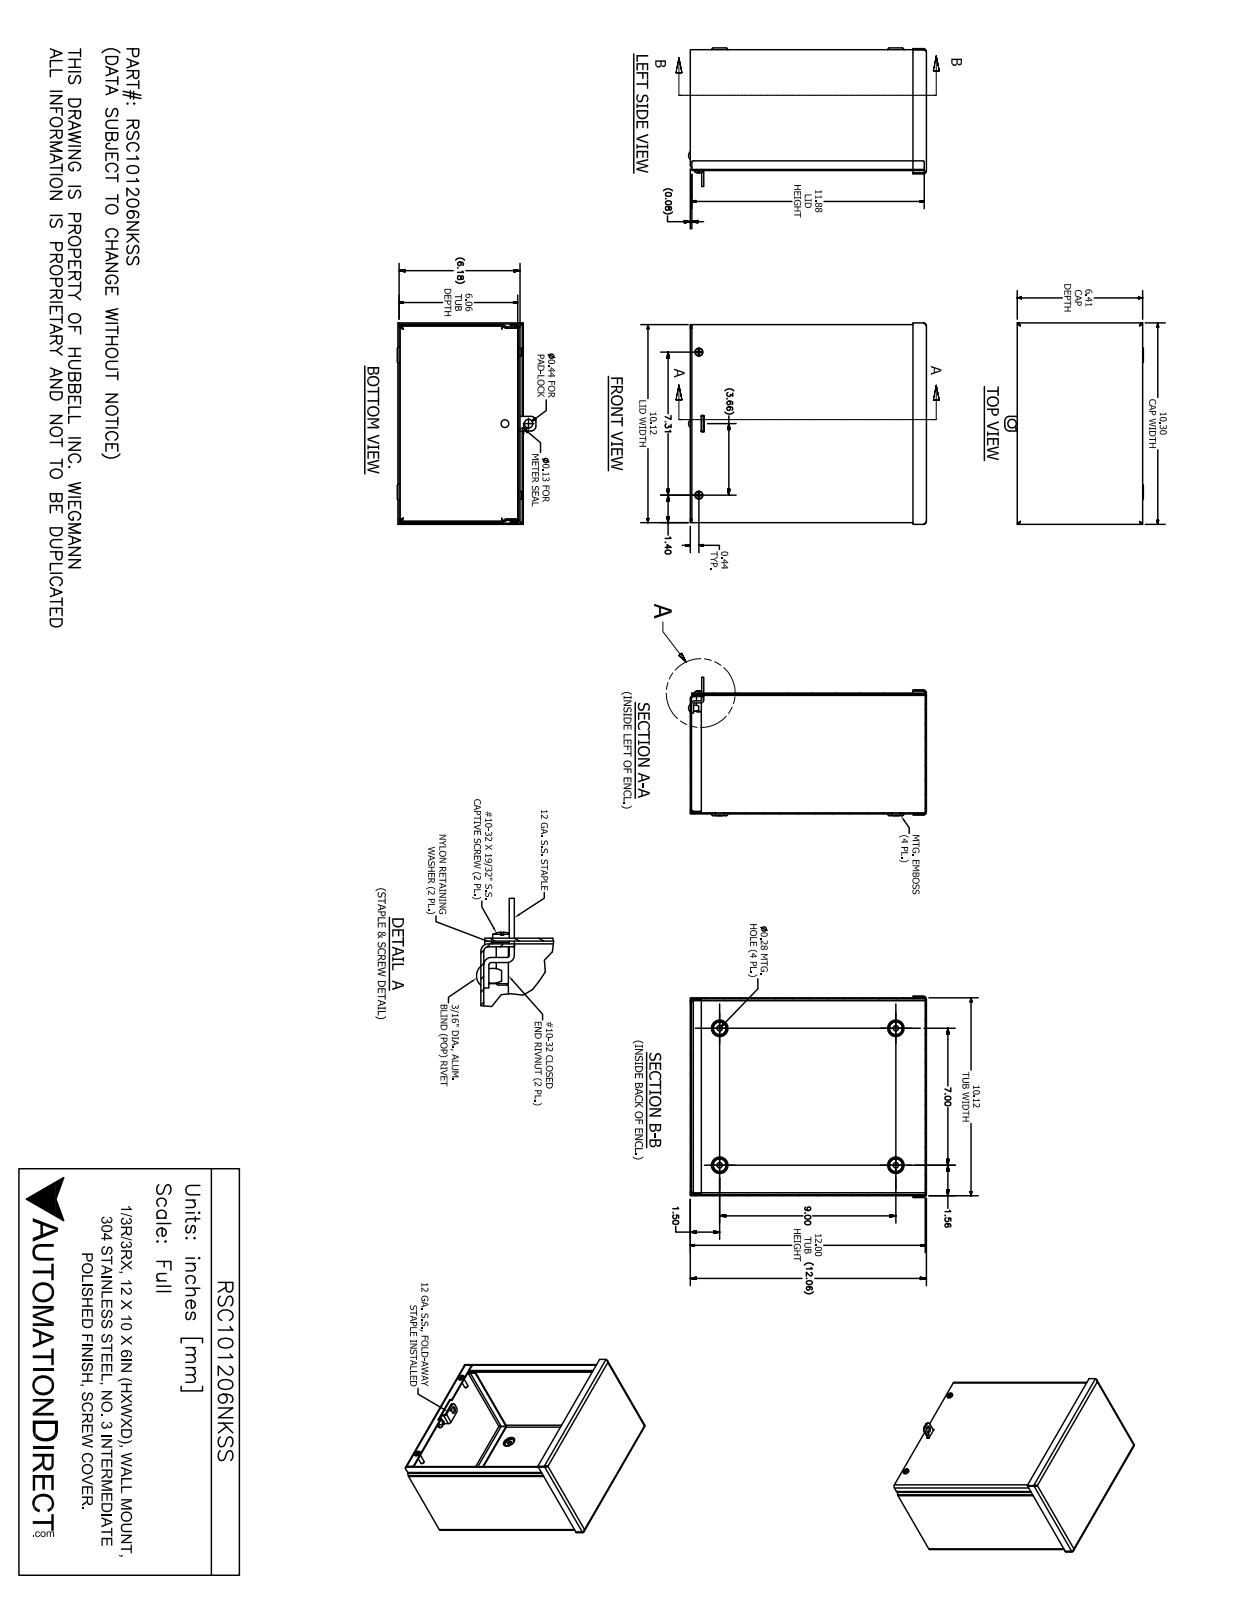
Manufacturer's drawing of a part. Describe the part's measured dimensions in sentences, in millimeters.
The part is named "RSC101206NKSS". Its 3-D file was written by "SolidWorks 2017 (AUTOMOTIVE_DESIGN)". It is 12 solids with 369 faces: 191 planar, 93 cylindrical and 85 other. Overall it measures 308.6 by 261.6 by 179.9 millimeters. Its volume is 539 500 cubic millimeters and its surface area 727 100 square millimeters. Round holes: 4 of diameter 6.4, 4 of diameter 7.1, 2 of diameter 4, 2 of diameter 5, 2 of diameter 6.5, 2 of diameter 7.1, 1 of diameter 3.2, 1 of diameter 5, 1 of diameter 5.1, 1 of diameter 11.1. Round bosses or shafts: 2 of diameter 11.5, 2 of diameter 10.3, 2 of diameter 6.3, 2 of diameter 4.2, 1 of diameter 4.7. Partial cylindrical surfaces (rounded edges, fillets, slot ends): 16 of radius 2.4, 16 of radius 3.9, 6 of radius 0.8, 4 of radius 6.4, 2 of radius 1.2, 2 of radius 1.3, 2 of radius 1.6, 2 of radius 2.3. The main face-to-face distances are 1.5, 155.4, 255.5, 156.9, 153.9, 304.8, 257, 254, 306.3, 303.3. The hole center spacings are 27.3, 28.1, 177.8, 183.8, 183.9, 185.8, 228.6, 255.6.
